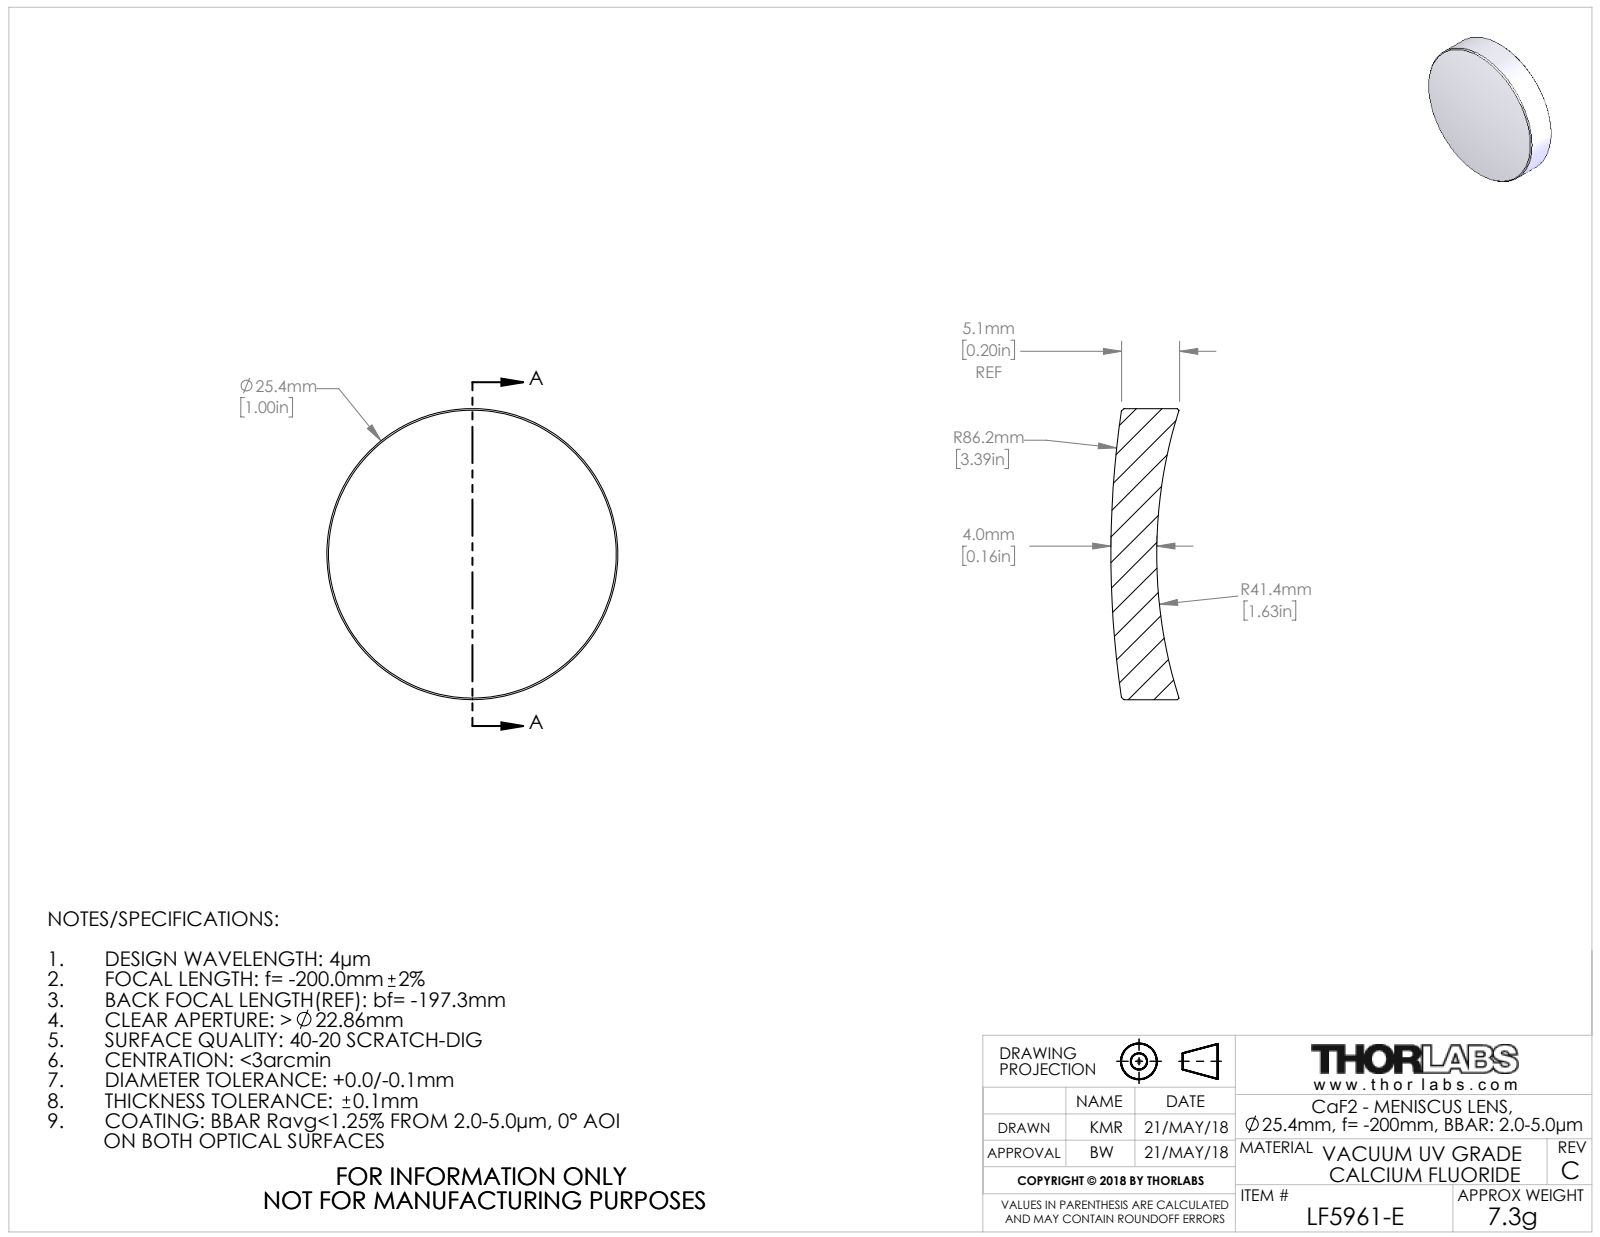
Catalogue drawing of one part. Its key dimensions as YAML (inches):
part_name: "20177-E0W"
step_written_by: "SolidWorks 2016 (CONFIG_CONTROL_DESIGN)"
units: inches
bodies: {solids: 1, faces: 10, planar: 0, cylindrical: 2, other: 8}
overall_size: [1, 1, 0.234]
volume: 0.14
surface_area: 2.191
round_bosses_or_shafts:
  - {diameter: 1, count: 1}
